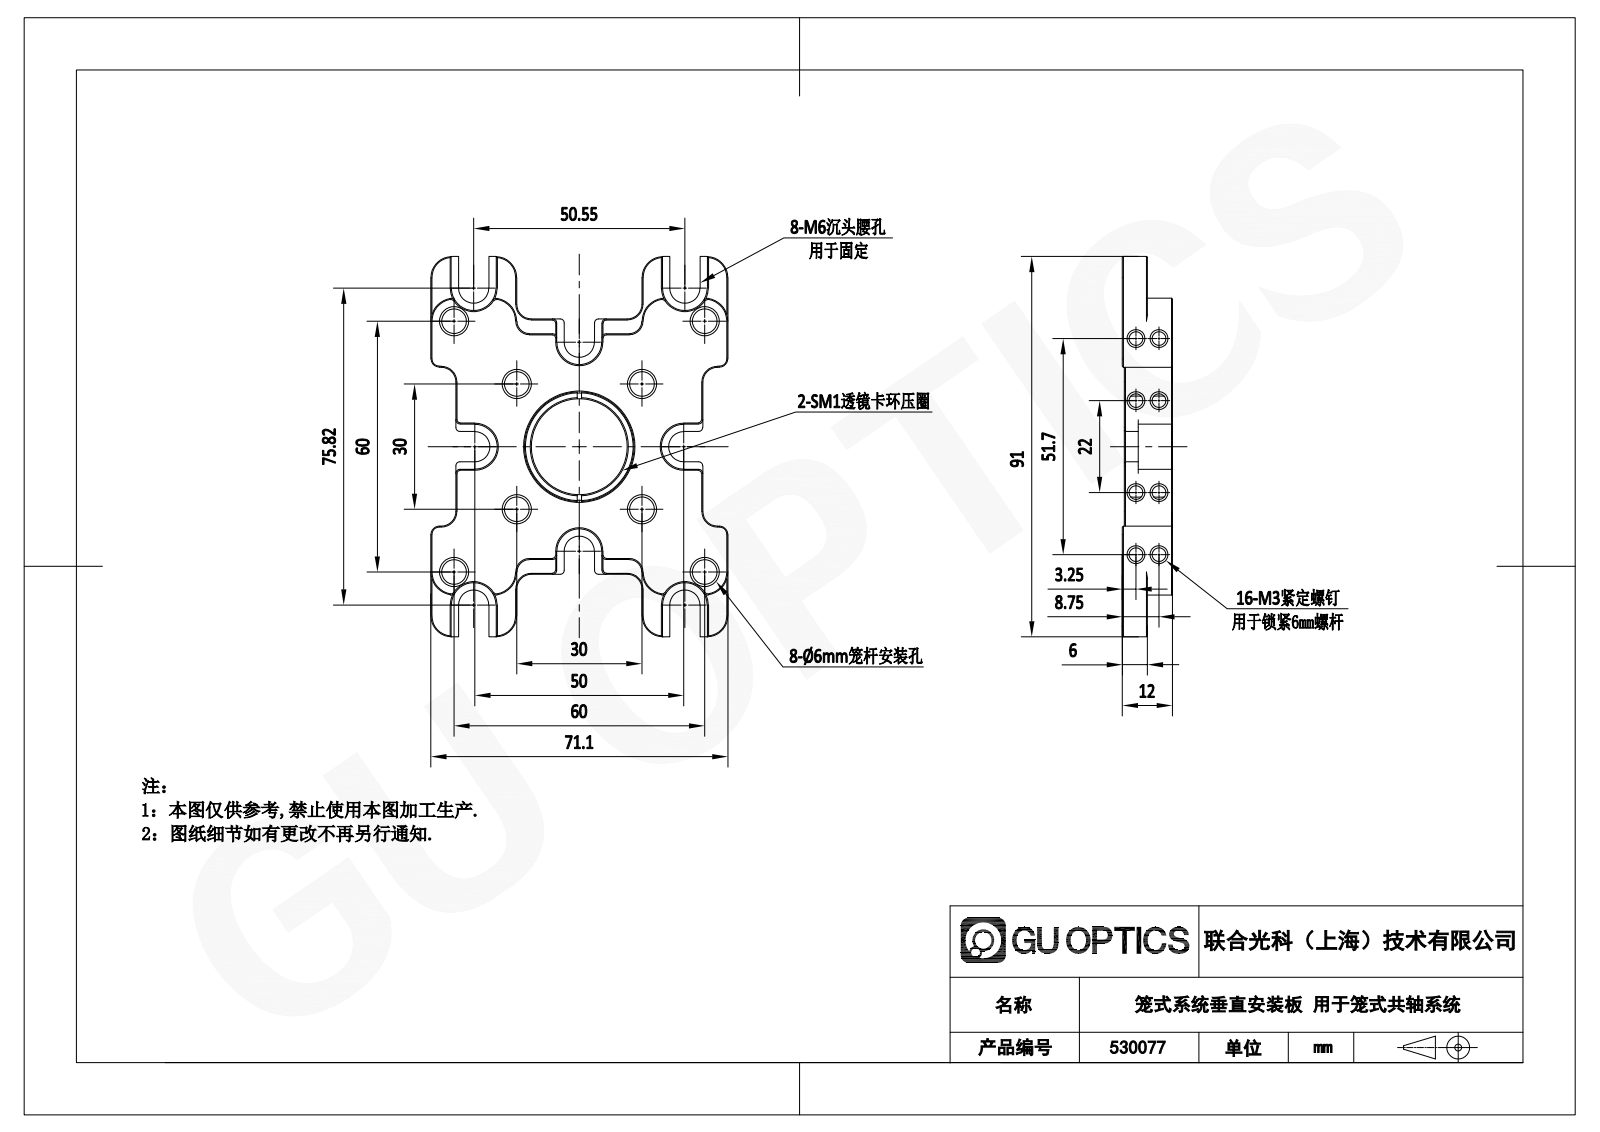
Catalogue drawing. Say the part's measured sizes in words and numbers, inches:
The part is named "530077". Its 3-D file was written by "SolidWorks 2020 (CONFIG_CONTROL_DESIGN)". It is 0 solids with 583 faces: 252 planar, 109 cylindrical and 222 other. Overall it measures 3.583 by 2.799 by 0.472 inches. Round holes: 8 of diameter 0.13, 8 of diameter 0.236, 1 of diameter 0.906, 1 of diameter 0.906, 1 of diameter 1.01. Round bosses or shafts: 1 of diameter 1.035. Partial cylindrical surfaces (rounded edges, fillets, slot ends): 28 of radius 0.039, 12 of radius 0.197, 8 of radius 0.138, 8 of radius 0.143, 8 of radius 0.213, 8 of radius 0.219, 4 of radius 0.079, 4 of radius 0.118. The main face-to-face distances are 0.453, 0.472, 0.02, 0.236, 0.217, 0.323, 0.087, 0.13, 0.15, 2.563. The hole center spacings are 0.835, 1.867, 1.67, 0.217, 0.585, 0.624, 1.181, 1.451.
